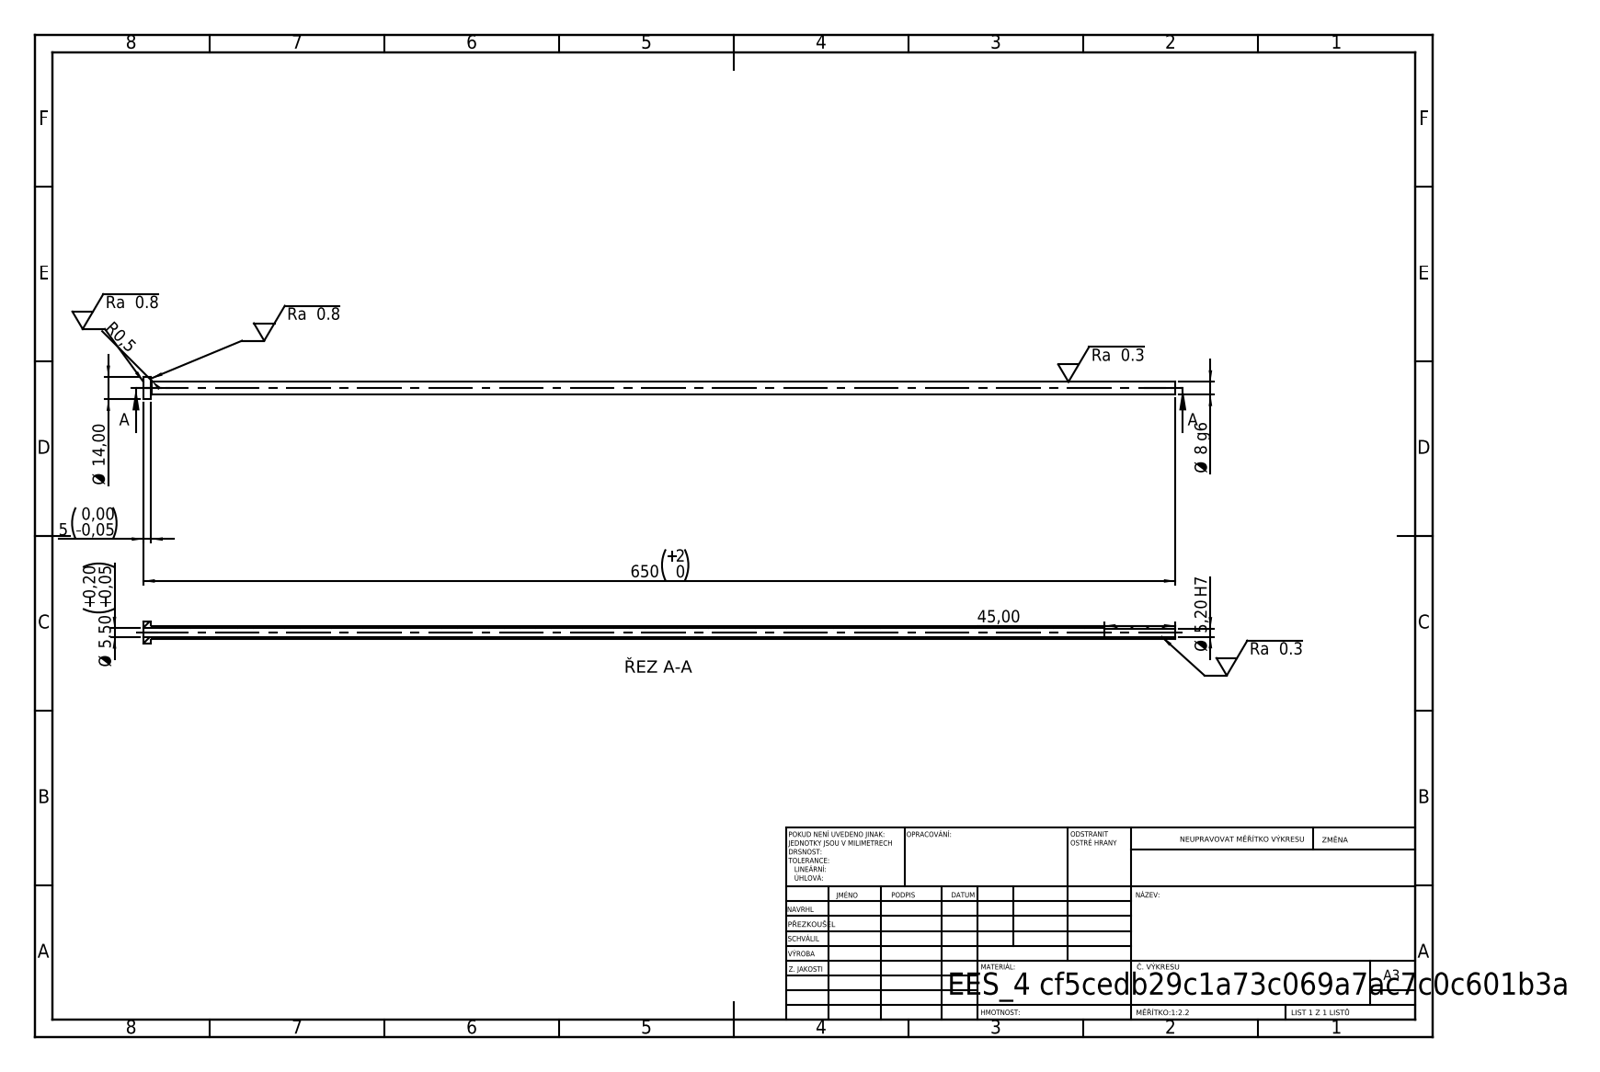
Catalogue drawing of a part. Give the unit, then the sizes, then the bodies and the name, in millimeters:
Units: millimetres
Overall size (bounding box): 650 × 14 × 14
Round holes (diameter × count): ⌀5.2 ×1, ⌀5.5 ×1
Round bosses / shafts (diameter × count): ⌀14 ×1, ⌀8 ×1
Main face-to-face distances: 5, 650, 645, 605, 600, 45
Volume: 17 863 mm³ · Surface area: 27 879 mm²
Bodies: 1 solid, 14 faces (4 planar, 8 cylindrical, 2 other)
STEP written by: SolidWorks 2019 (CONFIG_CONTROL_DESIGN)
